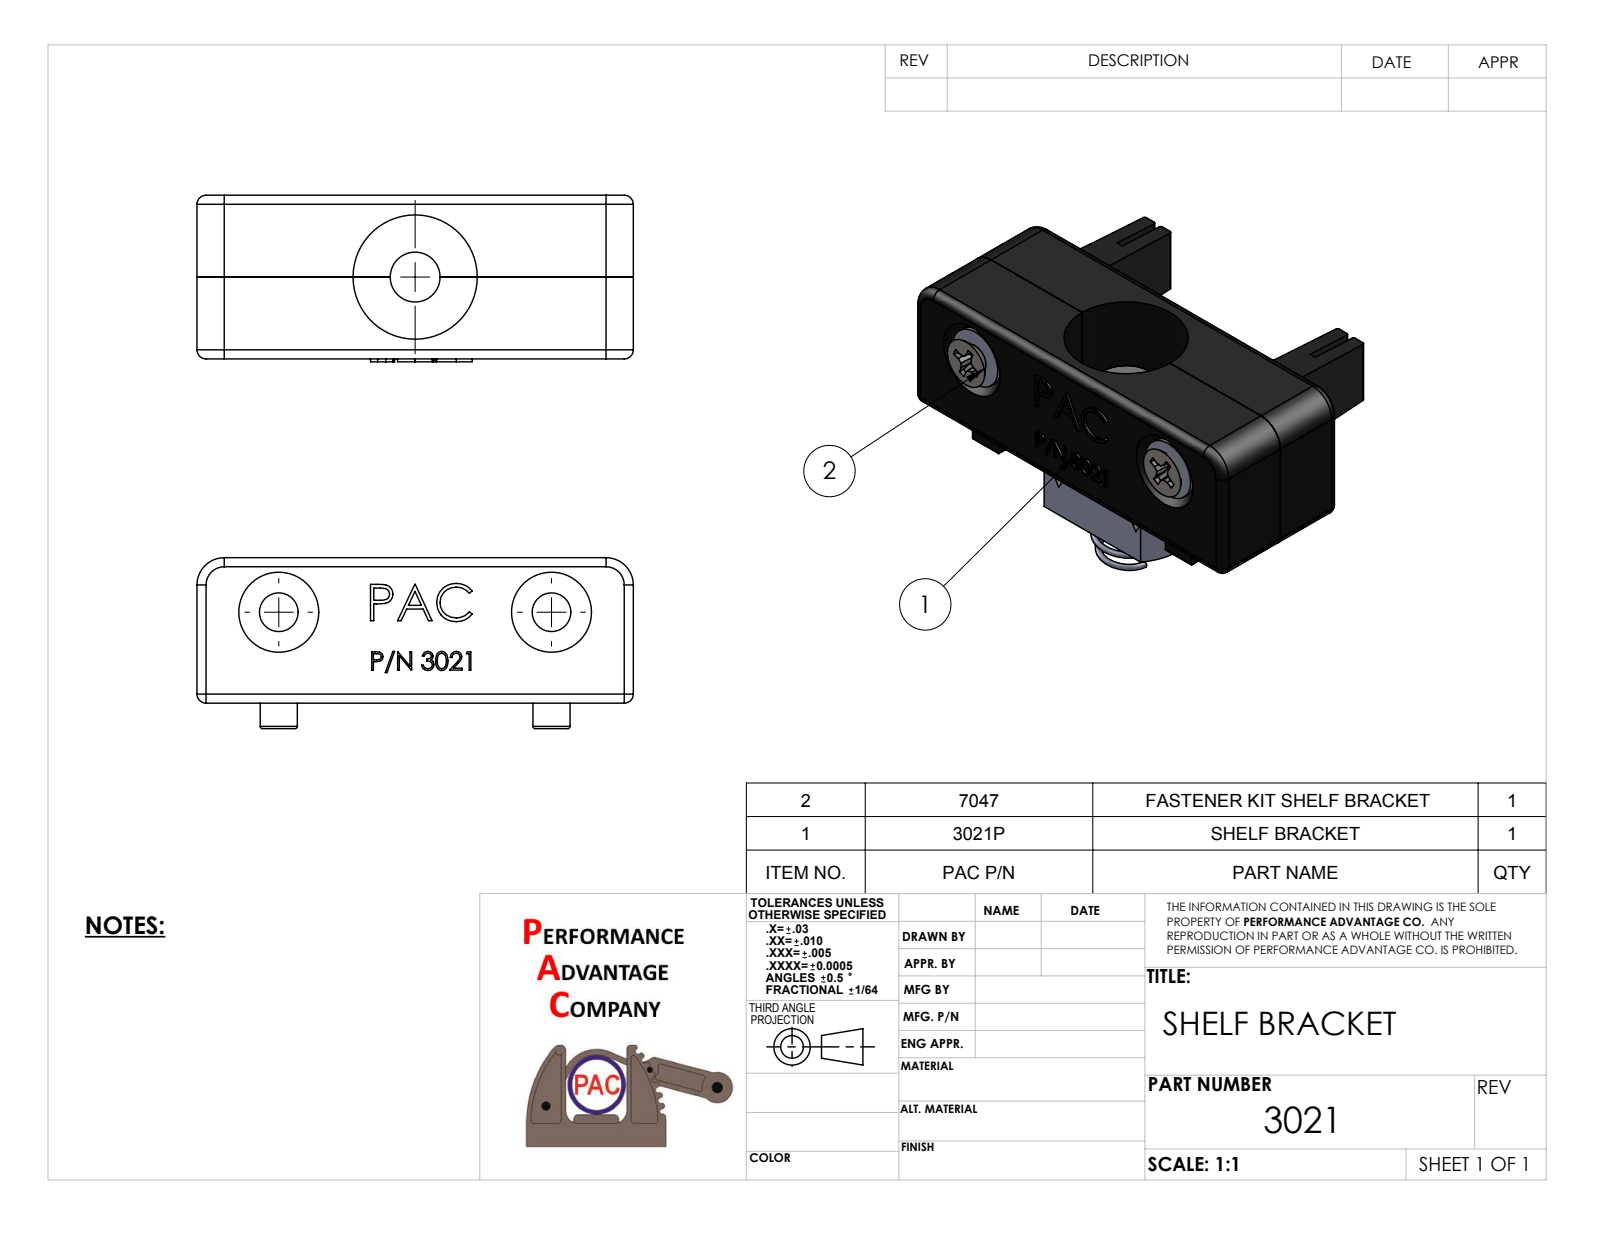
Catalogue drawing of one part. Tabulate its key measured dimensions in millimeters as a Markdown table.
| quantity | value |
| --- | --- |
| part name | 3021 |
| STEP written by | SolidWorks 2010 (CONFIG_CONTROL_DESIGN) |
| units | millimeters |
| bodies | 2 solids, 212 faces (104 planar, 42 cylindrical, 66 other) |
| overall size | 76.2 × 29.8 × 29.1 |
| volume | 46 700 mm³ |
| surface area | 14 960 mm² |
| round holes (diameter × count) | 6.8 × 2, 8.7 × 1, 21.7 × 1 |
| partial cylindrical surfaces (radius × count) | 1.6 × 8, 0.4 × 6, 1.6 × 2, 4.7 × 2 |
| main face-to-face distances | 14.3, 25.4, 28.6, 76.2, 9.5, 15.9, 4.4, 14, 29.8, 11 |
| hole center spacings | 47.6 |
